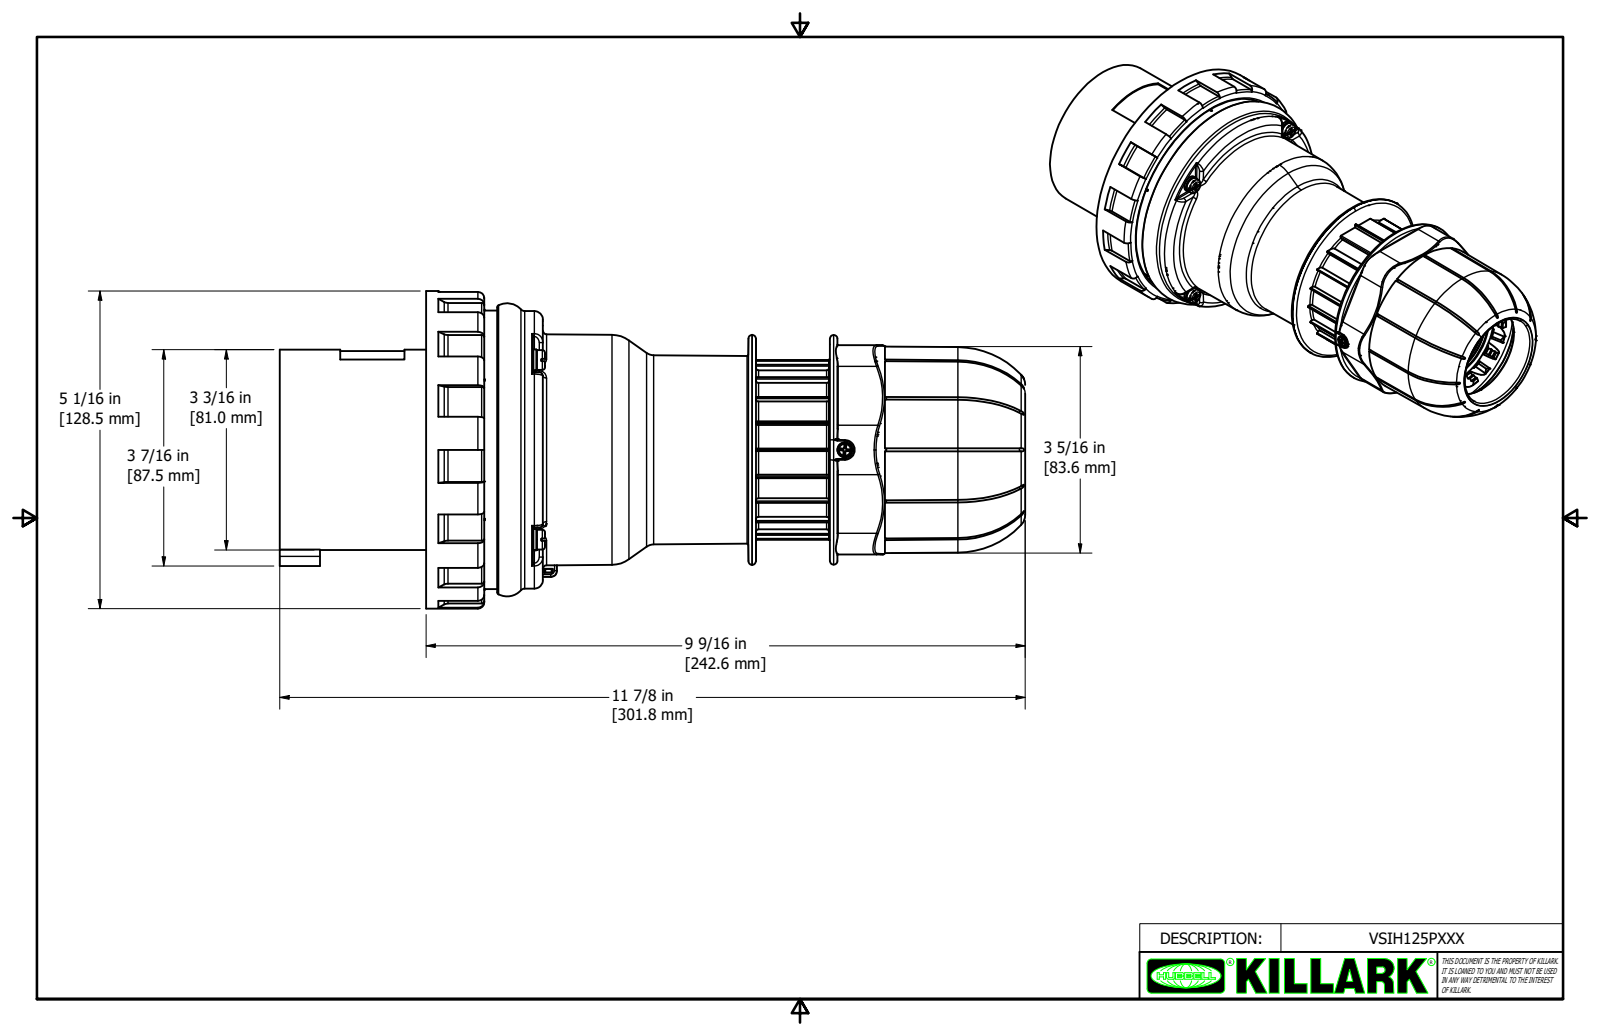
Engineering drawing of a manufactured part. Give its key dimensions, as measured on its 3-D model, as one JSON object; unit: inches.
{"part_name": "VSIH125PXXX (for customer)", "step_written_by": "Autodesk Inventor 2020 (AUTOMOTIVE_DESIGN)", "units": "inches", "bodies": {"solids": 1, "faces": 726, "planar": 184, "cylindrical": 230, "other": 312}, "overall_size": [11.88, 5.059, 5.059], "volume_in3": 113.9, "surface_area_in2": 182.8, "round_holes": [[0.201, 4]], "round_bosses_or_shafts": [[0.339, 4], [0.315, 4], [0.169, 4], [5.059, 1], [4.437, 1], [4.419, 1], [3.661, 1], [3.189, 1]], "partial_cylinders_radius": [[0.008, 47], [0.016, 36], [0.059, 24], [0.024, 12], [0.02, 10], [0.012, 6], [0.669, 5], [0.039, 4]], "face_to_face_distances": [2.331, 11.88, 9.55, 8.768, 6.437, 3.112, 0.925, 3.256, 5.512, 8.624], "hole_center_spacings": [2.86, 2.861, 4.045]}
